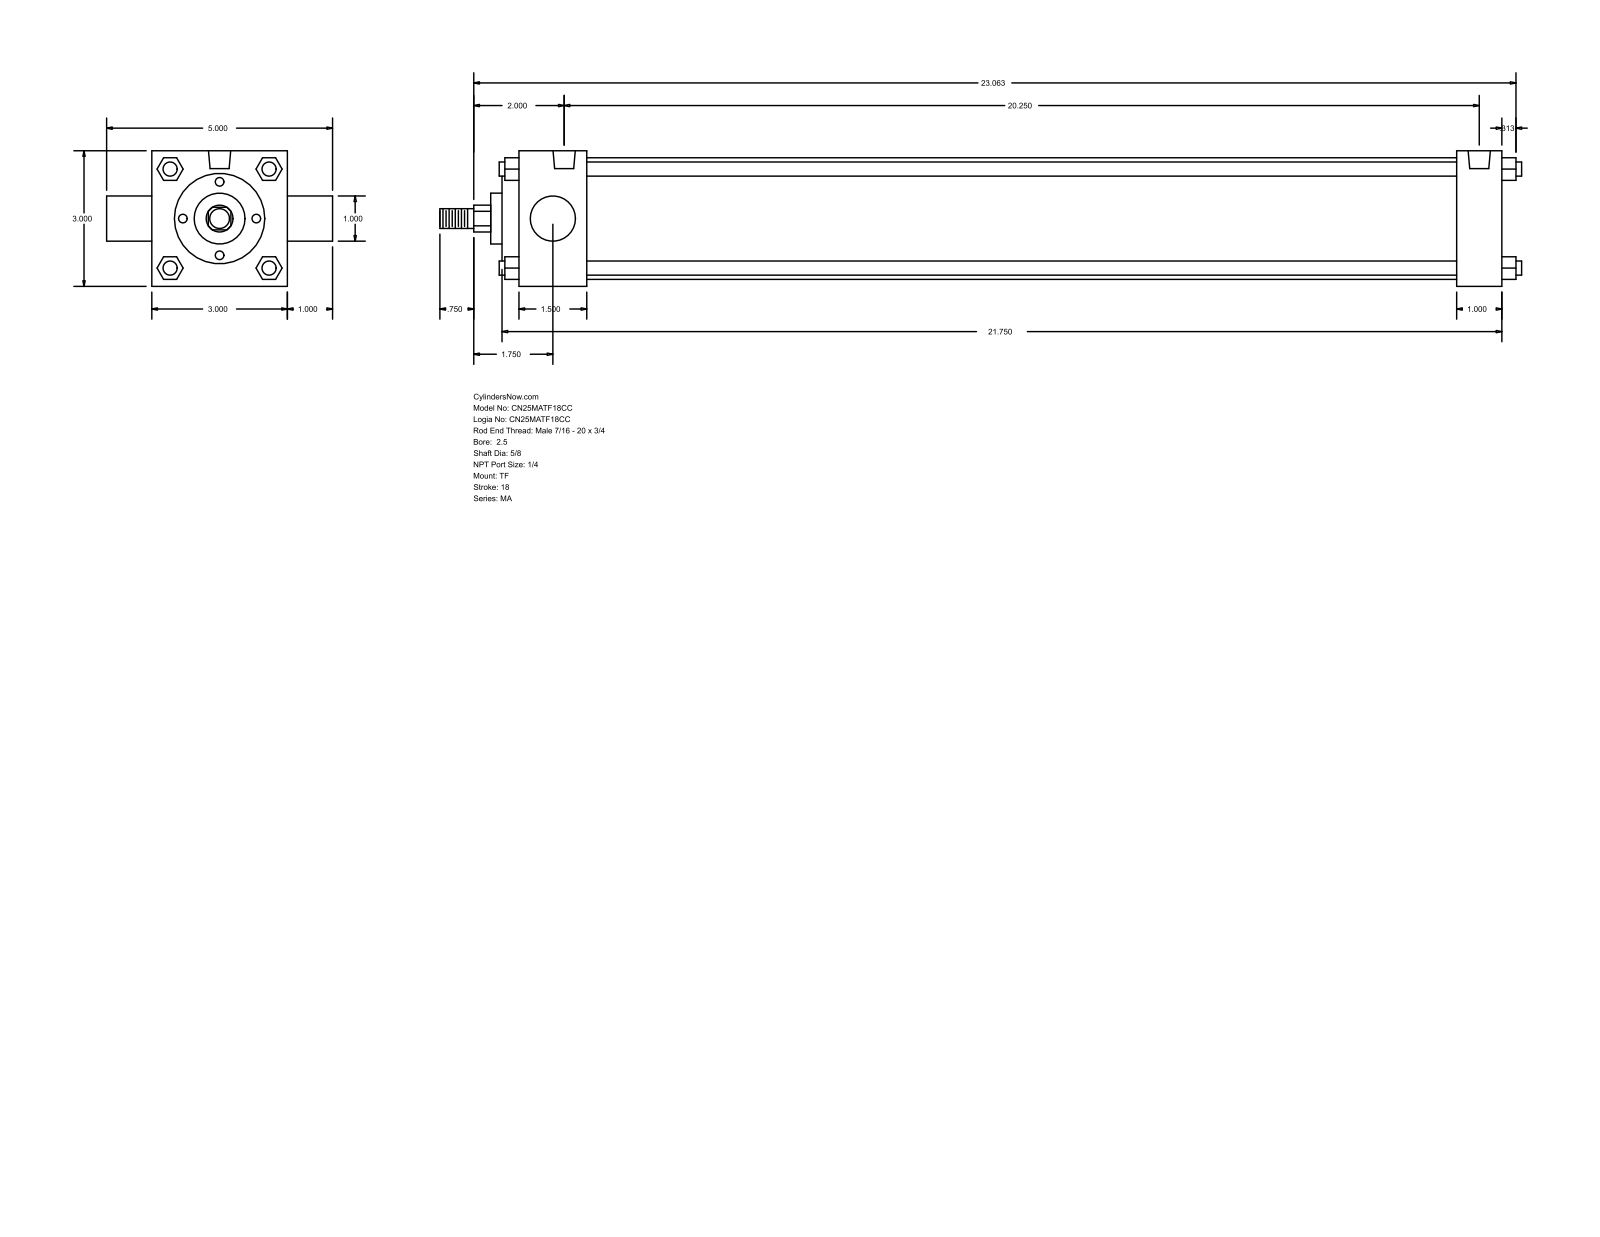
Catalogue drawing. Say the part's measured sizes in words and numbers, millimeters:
The part is named "MA_TF__0250_0.625". Its 3-D file was written by "GSSL Pune (CONFIG_CONTROL_DESIGN)". It is 0 solids with 122 faces: 93 planar, 29 cylindrical and 0 other. Overall it measures 608.01 by 127 by 76.2 millimeters. Round holes: 3 of diameter 7.94, 2 of diameter 12.49. Round bosses or shafts: 4 of diameter 7.94, 1 of diameter 68.33, 1 of diameter 50.8, 1 of diameter 28.57, 1 of diameter 25.4, 1 of diameter 15.88, 1 of diameter 11.11. Partial cylindrical surfaces (rounded edges, fillets, slot ends): 1 of radius 7.54. The main face-to-face distances are 76.2, 552.45, 25.4, 38.1, 527.05, 488.95, 514.35, 12.7, 9.52, 47.62. The hole center spacings are 514.35.
